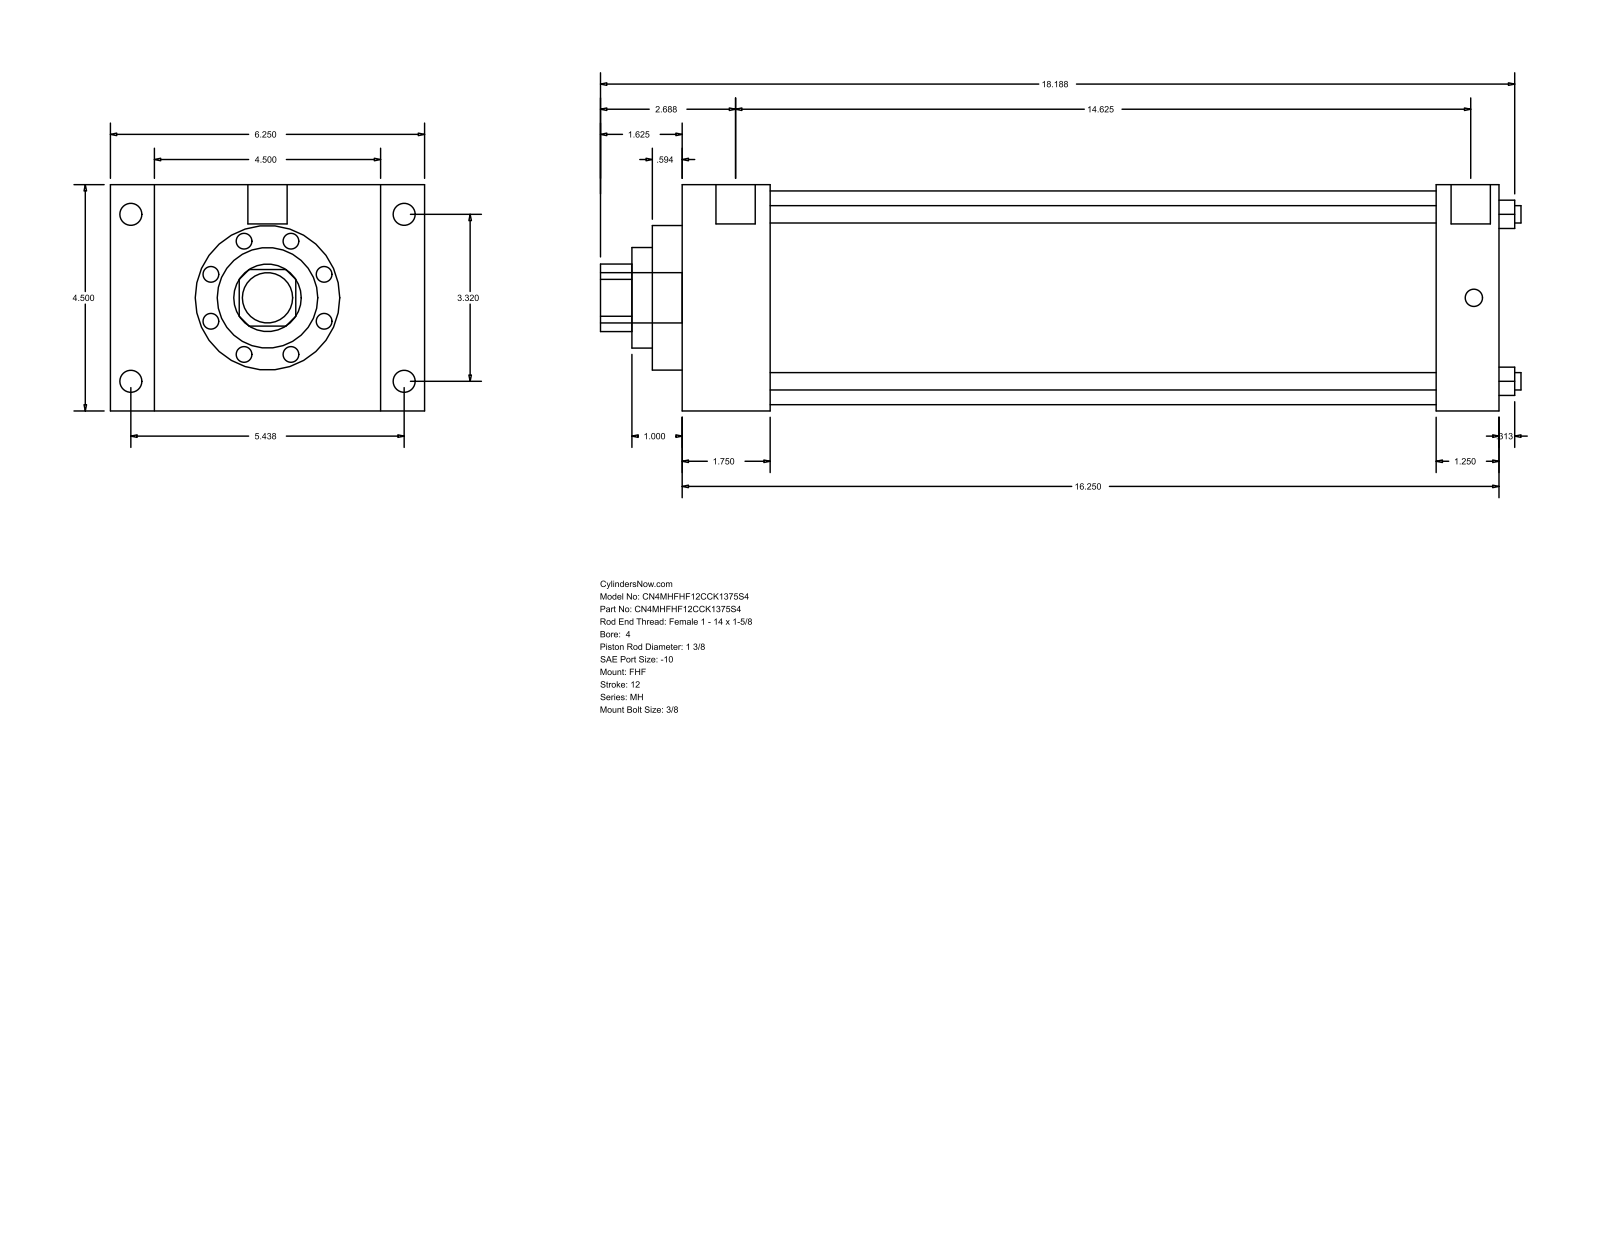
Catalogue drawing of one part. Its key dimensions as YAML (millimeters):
part_name: "MH_FHF__0400_1.375"
step_written_by: "GSSL Pune (CONFIG_CONTROL_DESIGN)"
units: millimeters
bodies: {solids: 0, faces: 90, planar: 61, cylindrical: 29, other: 0}
overall_size: [465.14, 158.75, 114.3]
round_holes:
  - {diameter: 8.76, count: 4}
  - {diameter: 34.92, count: 1}
  - {diameter: 50.8, count: 1}
  - {diameter: 73.03, count: 1}
  - {diameter: 107.95, count: 1}
round_bosses_or_shafts:
  - {diameter: 11.13, count: 4}
  - {diameter: 8.73, count: 4}
  - {diameter: 19.84, count: 2}
  - {diameter: 25.4, count: 1}
partial_cylinders:
  - {radius: 17.06, count: 1}
face_to_face_distances: [114.3, 412.75, 44.45, 368.3, 22.23, 136.53, 158.76, 381, 336.55, 31.75]
hole_center_spacings: [59.62, 84.32, 119.25]
